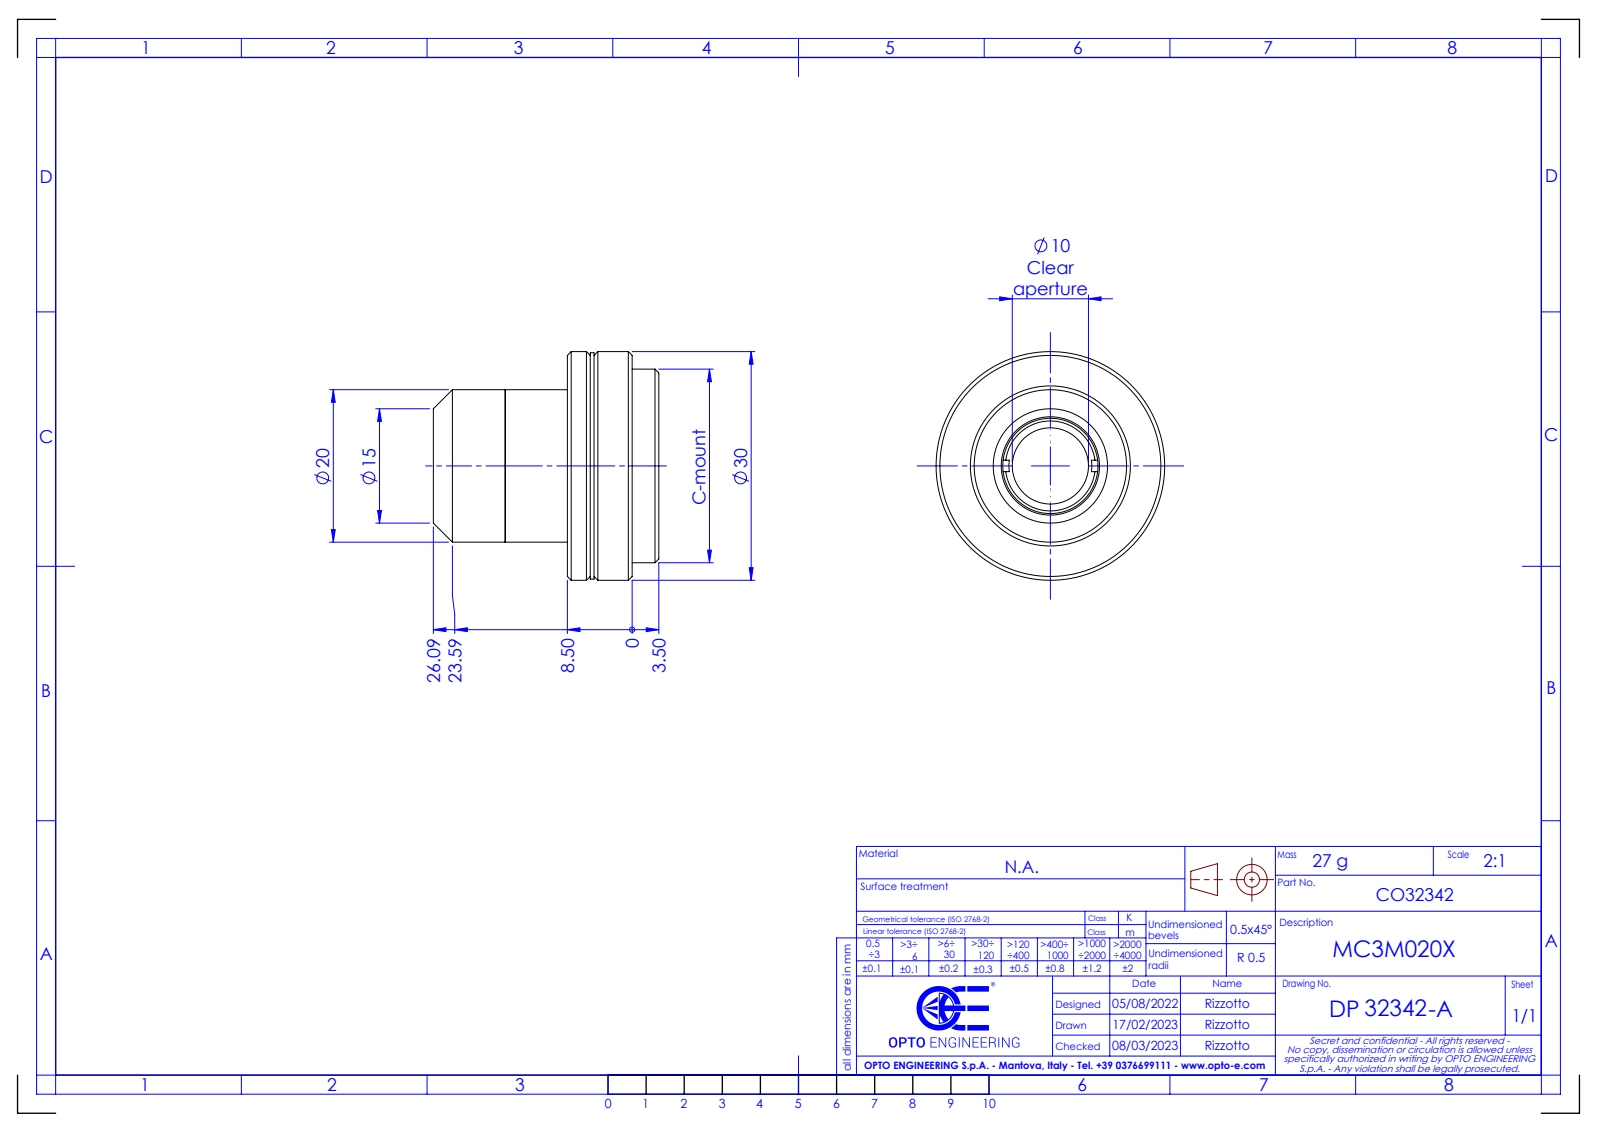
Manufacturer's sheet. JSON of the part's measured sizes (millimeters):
{"part_name": "DP32342-A_MC3M020X", "step_written_by": "SolidWorks 2021 (CONFIG_CONTROL_DESIGN)", "units": "millimeters", "bodies": {"solids": 0, "faces": 68, "planar": 18, "cylindrical": 24, "other": 26}, "overall_size": [30, 30, 29.59], "round_holes": [[10, 1], [12.5, 1], [15.5, 1], [16.5, 1], [18, 1]], "round_bosses_or_shafts": [[30, 1], [29.7, 1], [25.4, 1], [20, 1]], "face_to_face_distances": [8.5, 3.5, 5, 3, 0.5, 5.5, 12, 9, 0.66, 3.66]}
